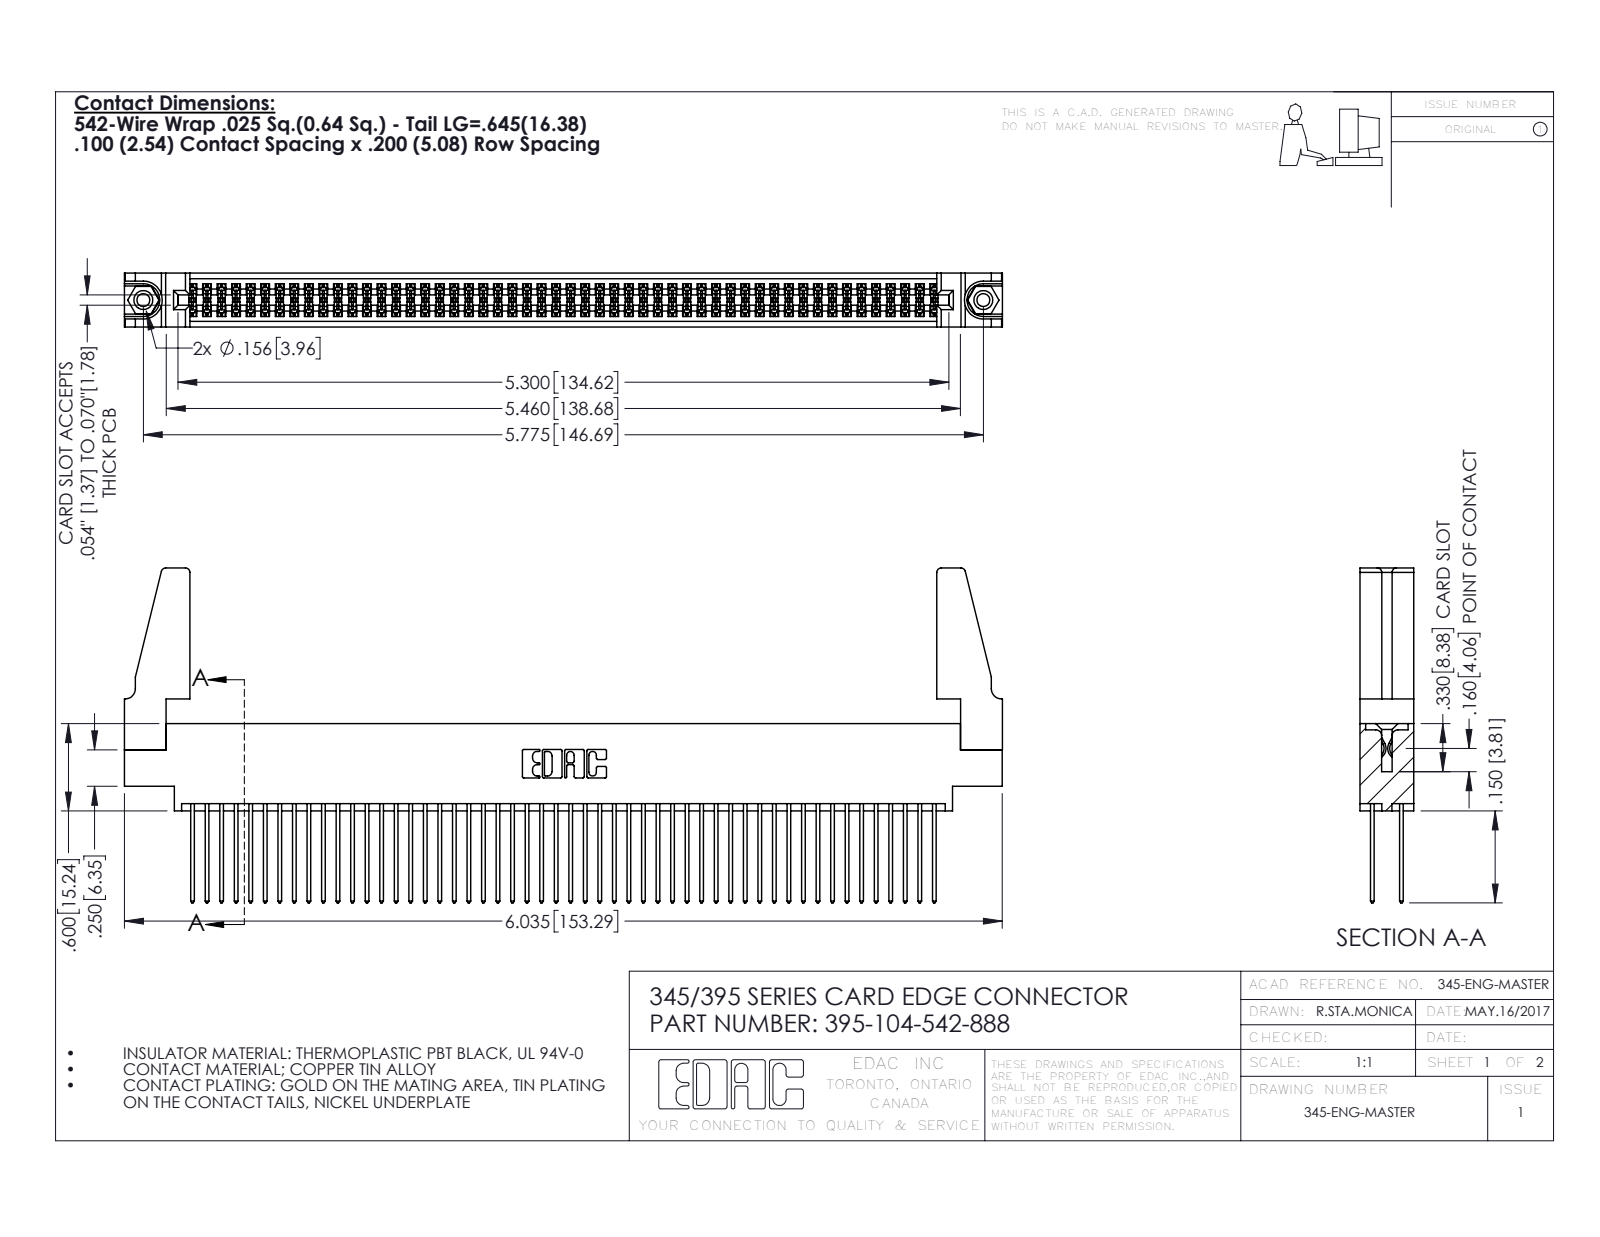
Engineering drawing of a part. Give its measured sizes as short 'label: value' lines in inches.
name: 345-292-001_345-293-142; 345 Part_0.170 Offset - 0.156 Dia-TH; 395-104-542-888; 345-250-001_345-250-001-102 (+1 more)
written by: SolidWorks 2016 (CONFIG_CONTROL_DESIGN)
unit: in
bodies: 109 solids, 5454 faces (3588 planar, 1850 cylindrical, 16 other)
size: 6.036 × 2.302 × 0.37
volume: 1.136 in³; area: 44.06 in²
holes: 2× ⌀0.089, 2× ⌀0.125, 2× ⌀0.156, 1× ⌀0.064
bosses: 2× ⌀0.155
rounds: 156× R0.006, 104× R0.01, 22× R0.01, 8× R0.03, 6× R0.007, 6× R0.031, 3× R0.026, 2× R0.014
face distances: 0.072, 0.298, 0.098, 0.272, 0.025, 0.2, 0.37, 0.225, 0.175, 0.149
hole spacings: 0.27, 5.539, 5.775
